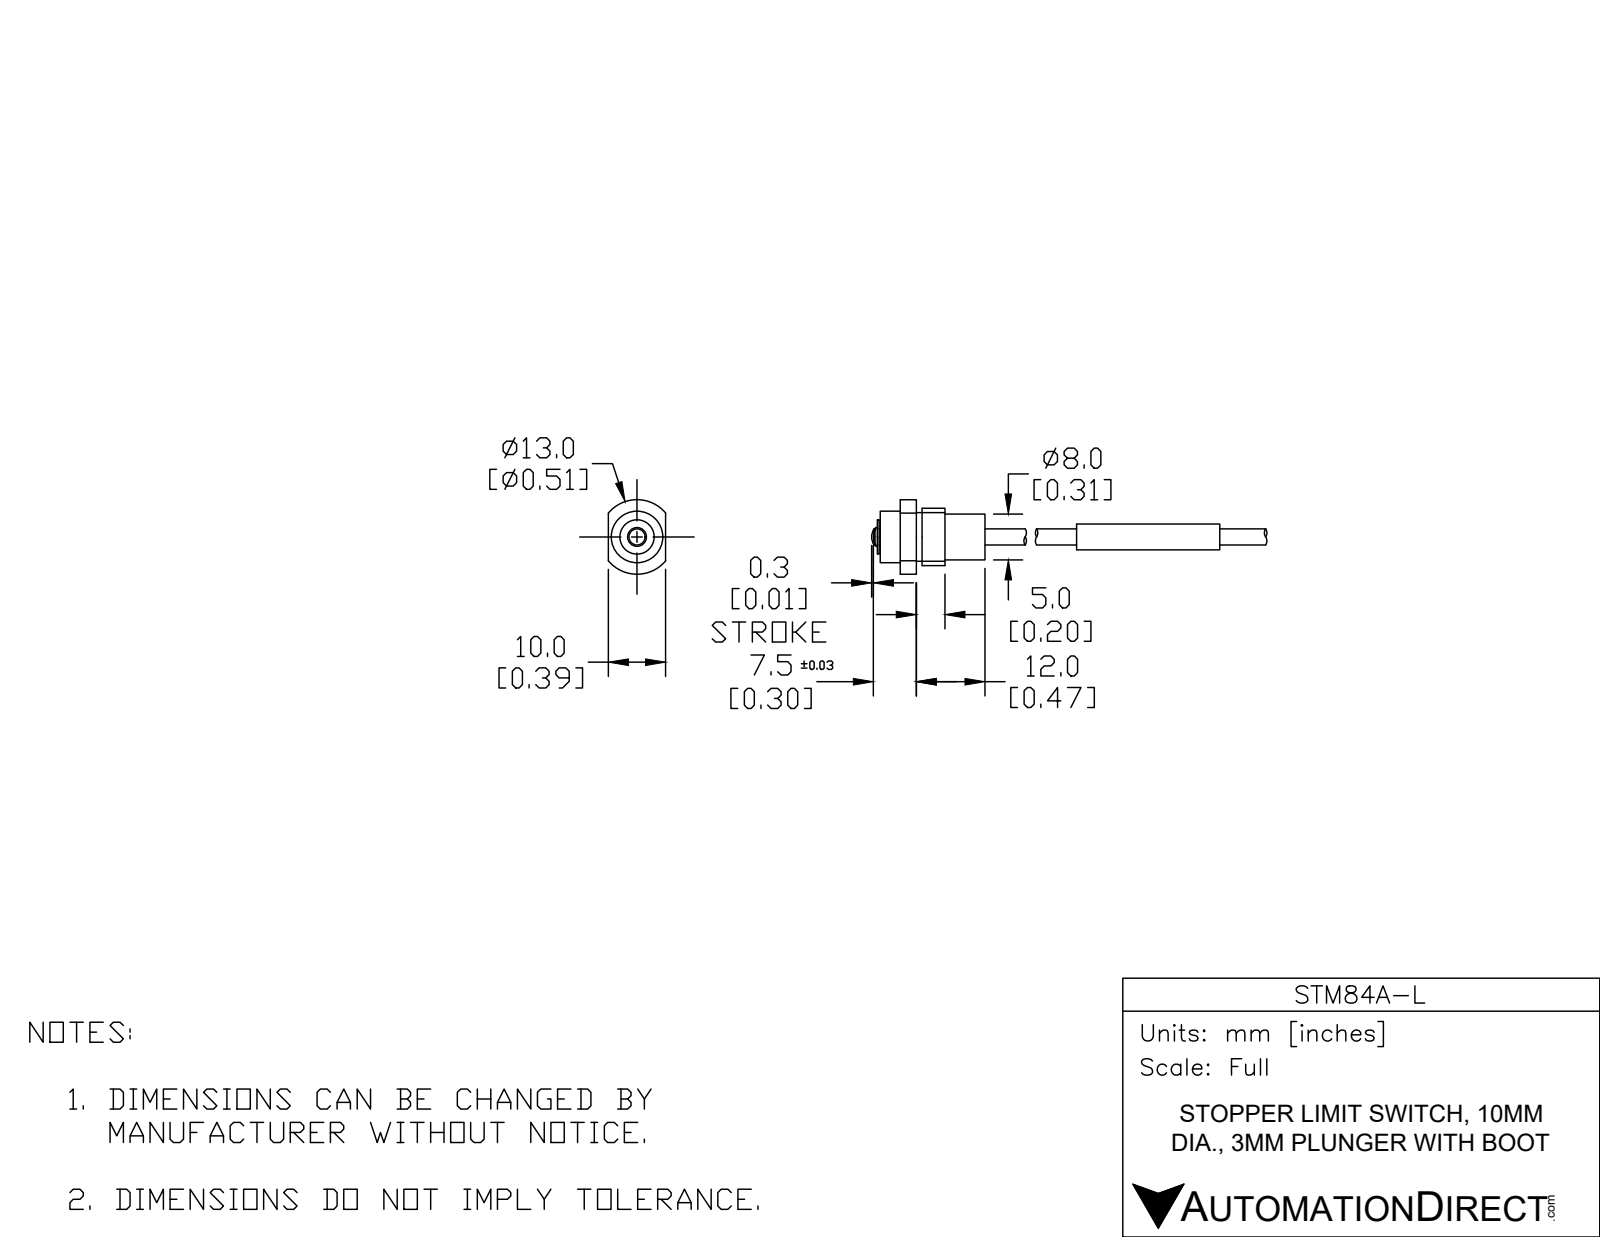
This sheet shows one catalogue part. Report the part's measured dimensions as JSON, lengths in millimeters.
{"part_name": "STM84A-L", "step_written_by": "SolidWorks 2017 (CONFIG_CONTROL_DESIGN)", "units": "millimeters", "bodies": {"solids": 2, "faces": 52, "planar": 17, "cylindrical": 28, "other": 7}, "overall_size": [70.8, 13, 10], "volume_mm3": 1770, "surface_area_mm2": 1511, "round_bosses_or_shafts": [[10, 1], [9, 1], [8, 1], [6, 1], [4.5, 1], [2.8, 1]], "partial_cylinders_radius": [[6.5, 1]], "face_to_face_distances": [6.3, 3.5, 2.8, 18.3, 14.8, 12, 4, 7.8, 10, 6.8]}
